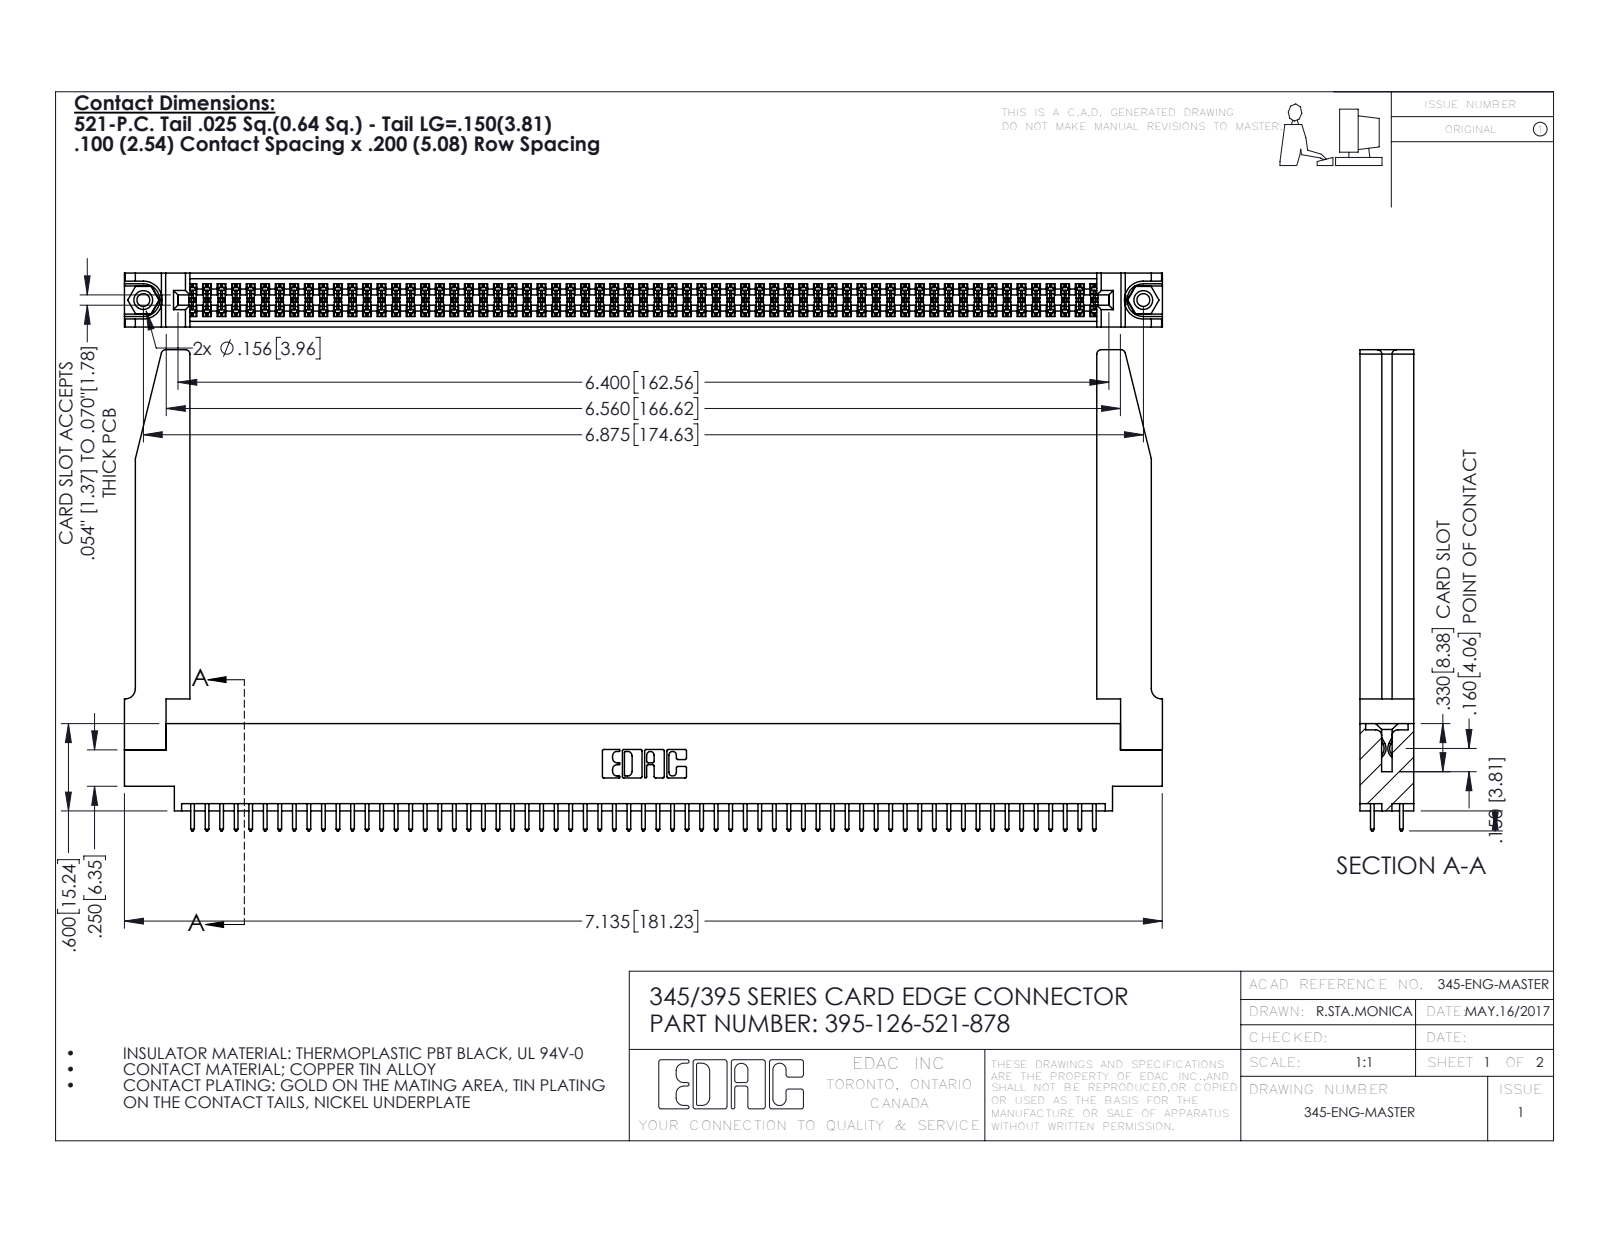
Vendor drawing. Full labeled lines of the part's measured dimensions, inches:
Part name (STEP PRODUCT): 395-126-521-878; 345-292-001_345-293-121; 345-250-001_345-250-001-102; 345 Part_0.170 Offset - 0.156 Dia-TH (+1 more)
STEP written by: SolidWorks 2016 (CONFIG_CONTROL_DESIGN)
Units: inches
Bodies: 131 solids, 6664 faces (4384 planar, 2228 cylindrical, 52 other)
Overall size (bounding box): 7.136 × 3.307 × 0.37
Volume: 1.55 in³ · Surface area: 51.34 in²
Round holes (diameter × count): ⌀0.089 ×2, ⌀0.125 ×2, ⌀0.156 ×2, ⌀0.064 ×1
Round bosses / shafts (diameter × count): ⌀0.155 ×2
Partial cylindrical surfaces — rounded edges, fillets, slot ends (radius × count): R0.006 ×189, R0.01 ×126, R0.01 ×22, R0.03 ×8, R0.007 ×6, R0.031 ×6, R0.026 ×3, R0.014 ×2
Main face-to-face distances: 0.072, 0.298, 0.37, 0.098, 0.272, 0.025, 0.2, 0.225, 0.175, 0.148
Hole centre spacings: 0.27, 6.639, 6.875
